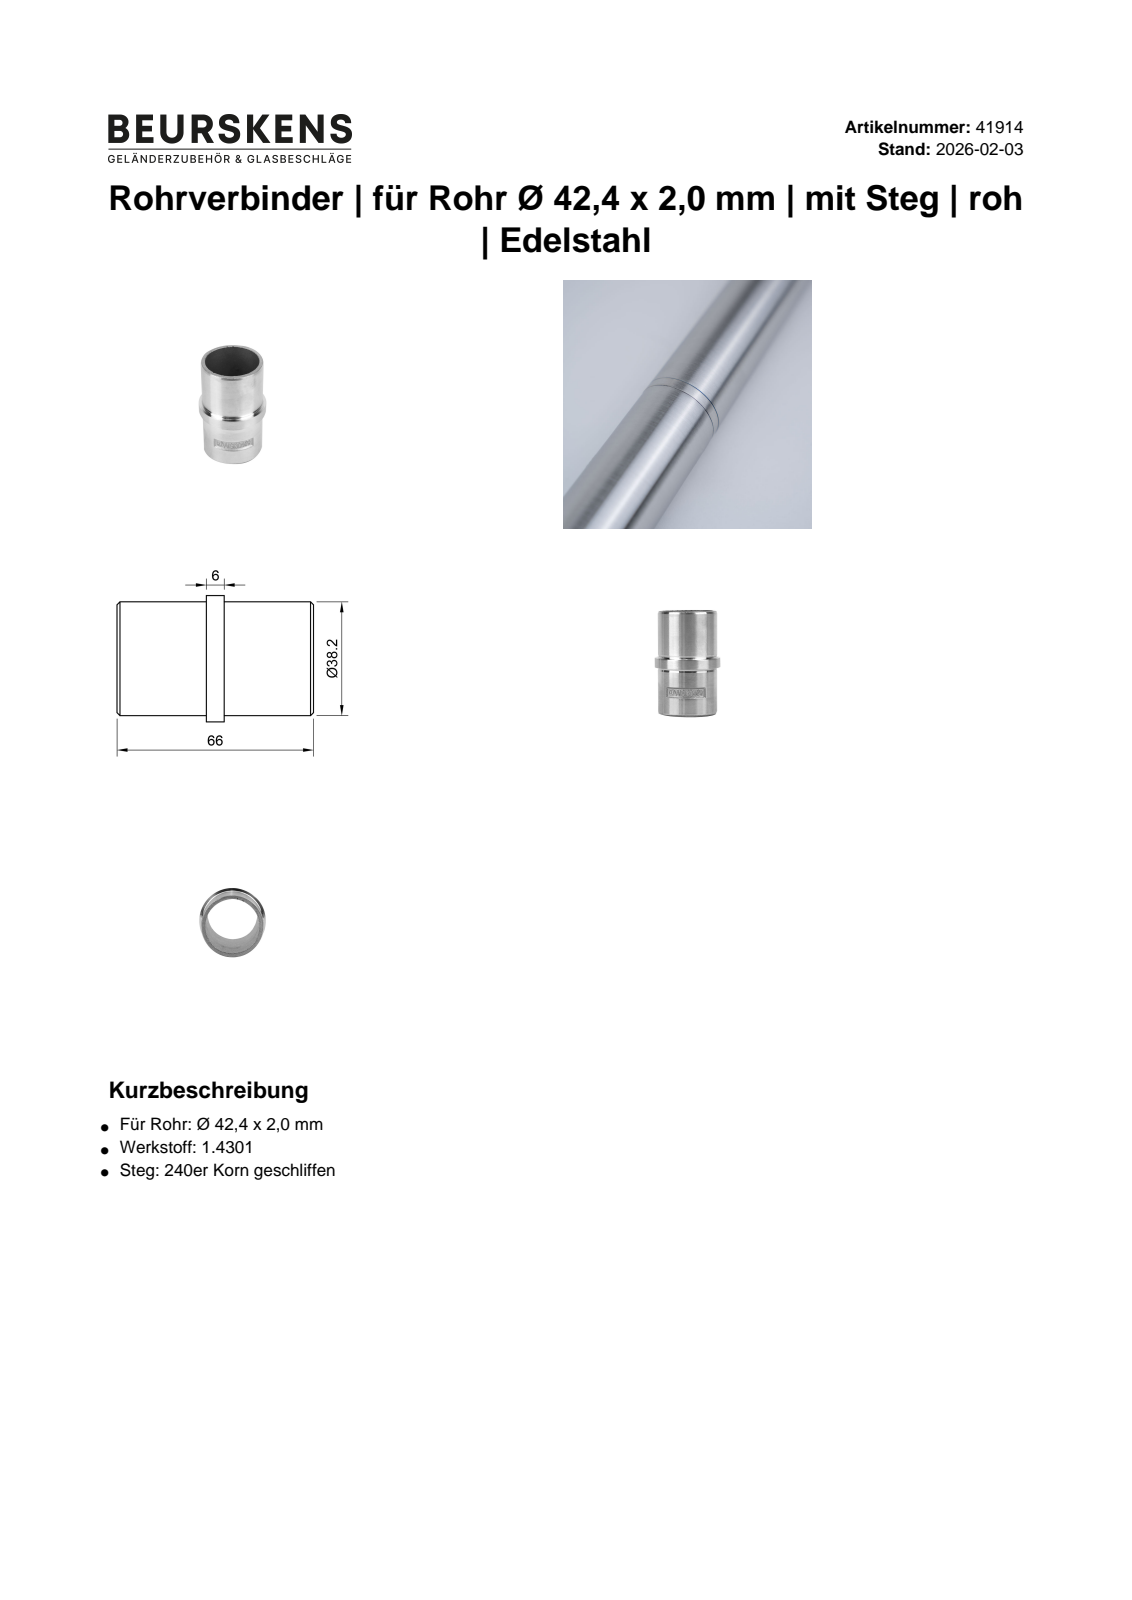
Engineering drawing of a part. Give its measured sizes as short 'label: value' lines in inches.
name: 41914
written by: Autodesk Inventor 2022 (AUTOMOTIVE_DESIGN)
unit: in
bodies: 1 solid, 8 faces (2 planar, 4 cylindrical, 2 other)
size: 2.598 × 1.669 × 1.669
volume: 0.561 in³; area: 25 in²
holes: 1× ⌀1.425
bosses: 1× ⌀1.669, 1× ⌀1.504
face distances: 0.236
